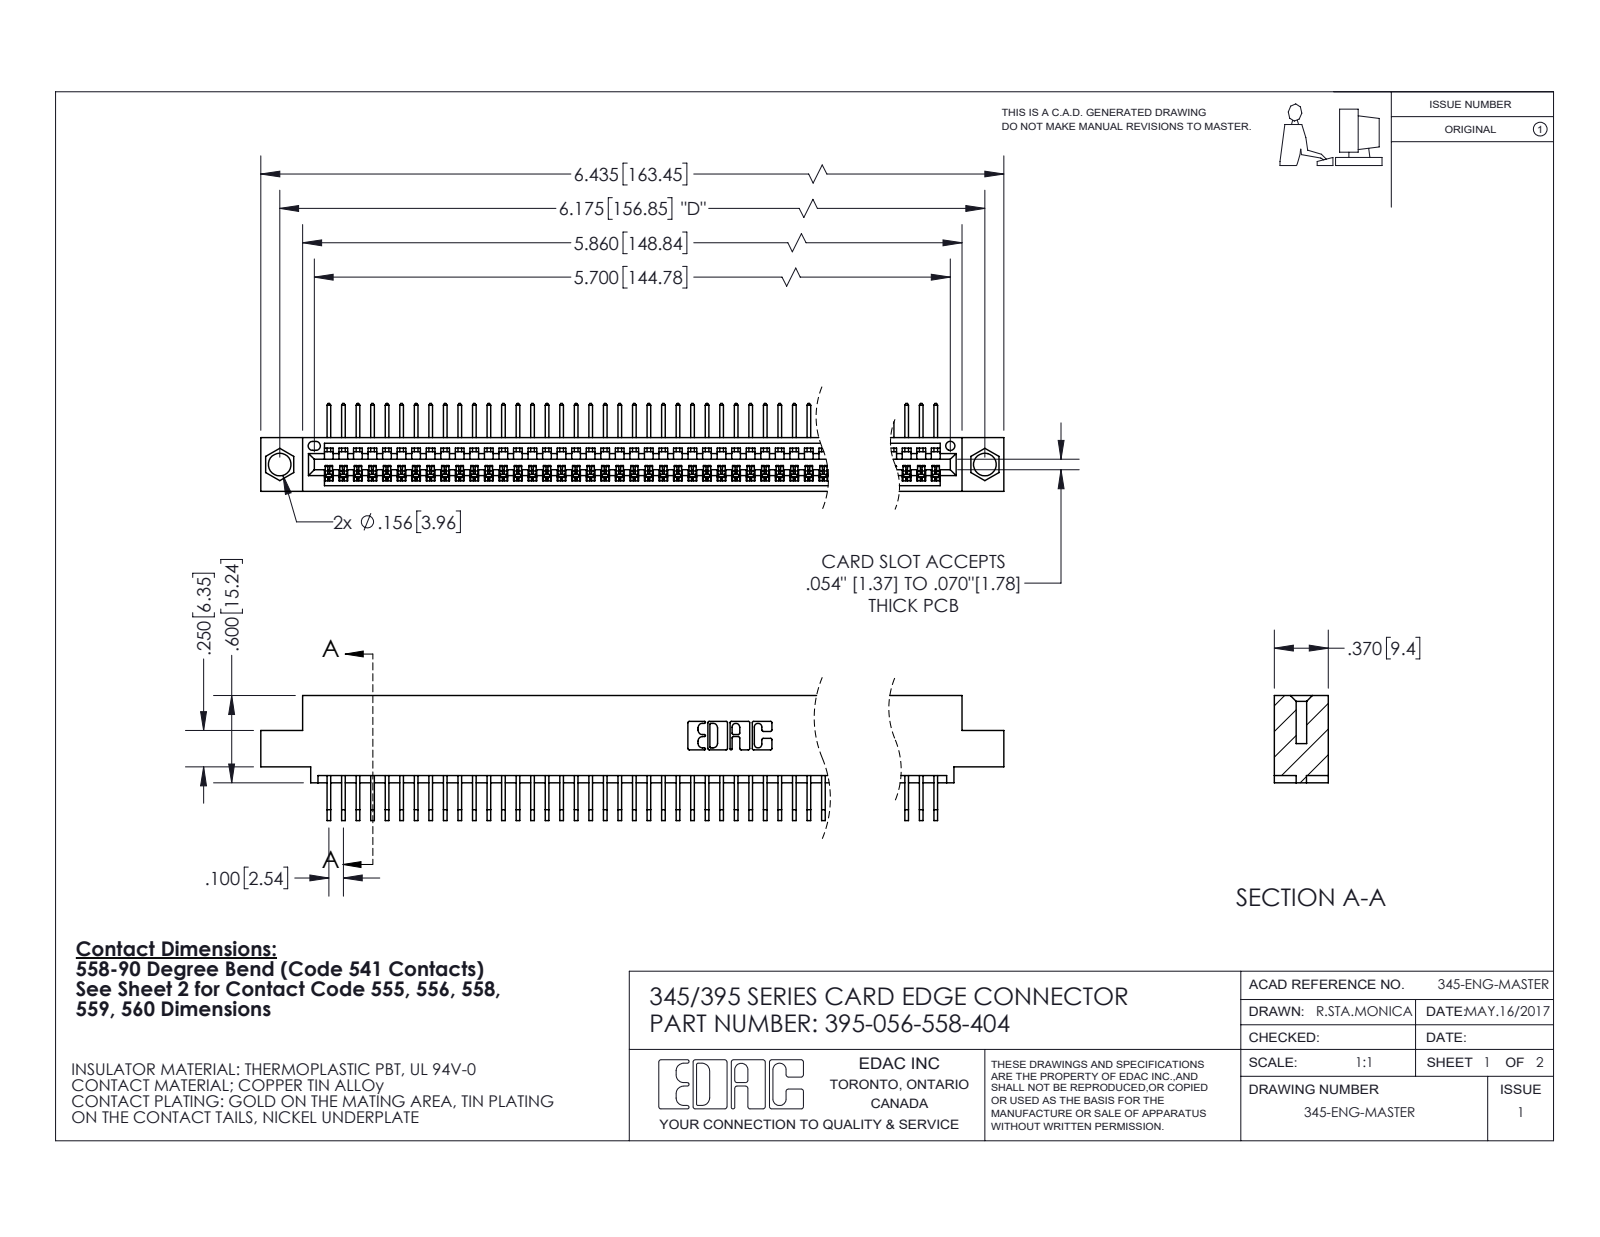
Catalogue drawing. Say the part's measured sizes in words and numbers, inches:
The part is named "345 Part_0.110 Offset - 0.156 Dia-TI; 345-292-001_558 Tail - 2; 395-056-558-404". Its 3-D file was written by "SolidWorks 2020 (CONFIG_CONTROL_DESIGN)". It is 57 solids with 3504 faces: 2450 planar, 1054 cylindrical and 0 other. Overall it measures 6.435 by 0.859 by 0.605 inches. Its volume is 0.955 cubic inches and its surface area 34.11 square inches. Round holes: 2 of diameter 0.156, 1 of diameter 0.064. Partial cylindrical surfaces (rounded edges, fillets, slot ends): 112 of radius 0.006, 22 of radius 0.01, 6 of radius 0.007, 6 of radius 0.031, 3 of radius 0.026, 2 of radius 0.031, 2 of radius 0.04, 1 of radius 0.014. The main face-to-face distances are 0.072, 0.298, 0.37, 0.2, 0.098, 0.272, 0.025, 0.225, 0.149, 0.072. The hole center spacings are 0.27, 5.939, 6.175.
